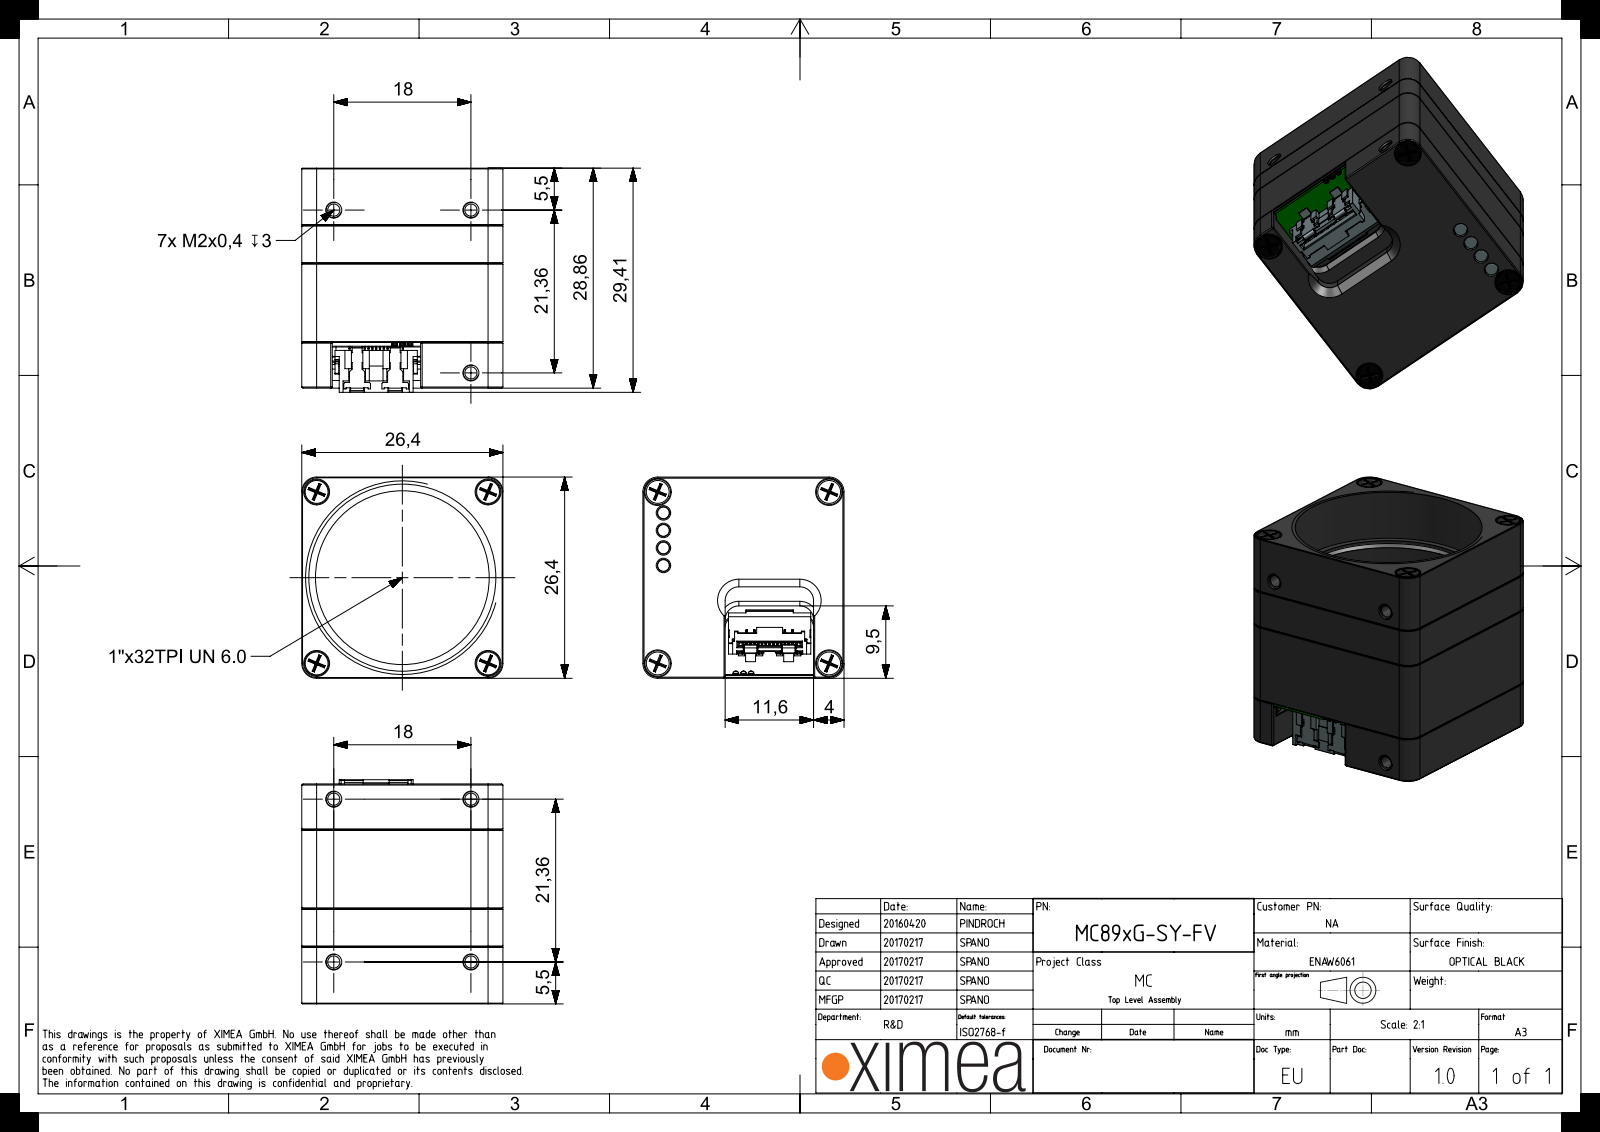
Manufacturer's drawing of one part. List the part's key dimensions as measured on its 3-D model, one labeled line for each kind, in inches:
Part name (STEP PRODUCT): MECH-O-RING-22X1-VI370; MT089xG-PR-SENSOR-PCA; FLT-BK7-AR2X-D25; SROB-M1.6x3-SLOT-STNLS (+8 more)
STEP written by: SIEMENS PLM Software NX 1907 (AUTOMOTIVE_DESIGN)
Units: inches
Bodies: 32 solids, 7179 faces (4927 planar, 1957 cylindrical, 295 other)
Overall size (bounding box): 1.158 × 1.039 × 1.039
Volume: 0.601 in³ · Surface area: 27.27 in²
Round holes (diameter × count): ⌀0.063 ×12, ⌀0.039 ×4, ⌀0.079 ×4, ⌀0.083 ×4, ⌀0.118 ×4, ⌀0.126 ×4, ⌀0.132 ×4, ⌀0.051 ×2, ⌀0.067 ×2, ⌀0.157 ×1, ⌀0.827 ×1, ⌀0.898 ×1
Round bosses / shafts (diameter × count): ⌀0.075 ×4, ⌀0.064 ×4, ⌀0.033 ×4, ⌀0.118 ×2, ⌀0.063 ×2, ⌀0.984 ×1, ⌀0.85 ×1
Partial cylindrical surfaces — rounded edges, fillets, slot ends (radius × count): R0.039 ×26, R0.013 ×16, R0.006 ×14, R0.004 ×12, R0.015 ×12, R0.01 ×8, R0.02 ×8, R0.051 ×8
Main face-to-face distances: 0.039, 0.142, 1.039, 0.27, 0.1, 0.181, 0.451, 0.412, 0.408, 0.266
Hole centre spacings: 0.626, 0.886, 0.091, 0.148, 0.181, 0.531, 0.709, 0.738
